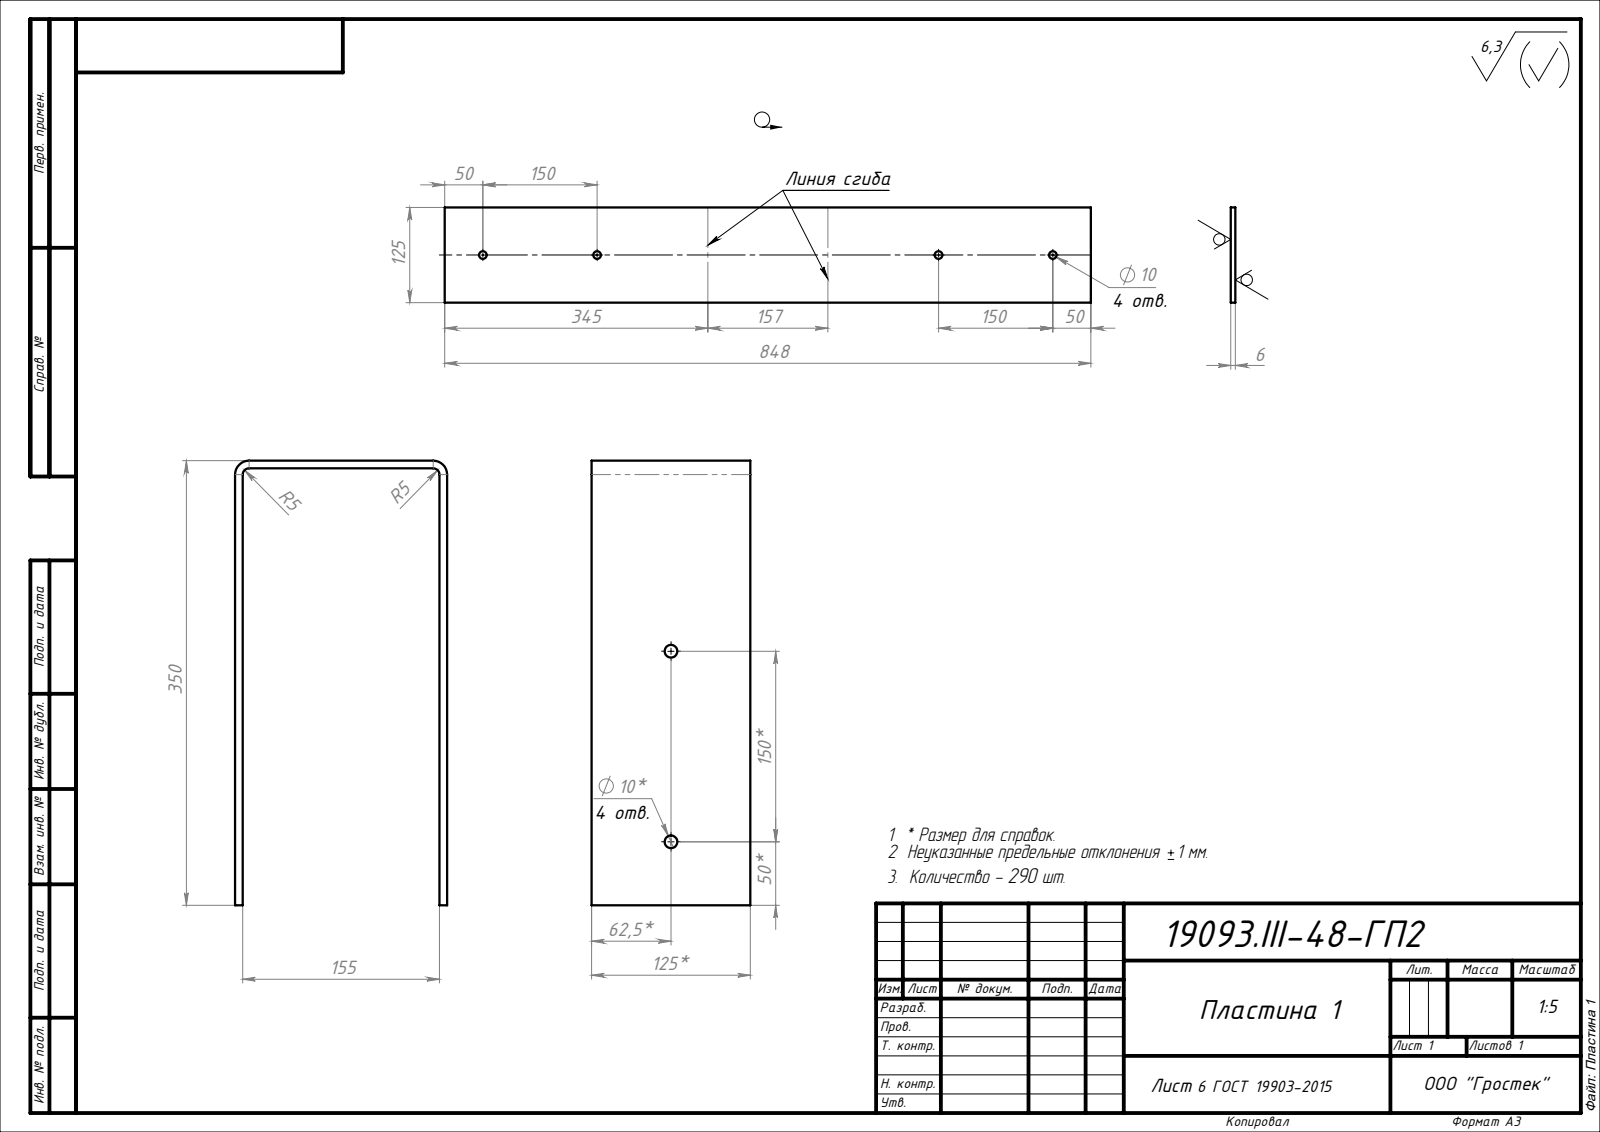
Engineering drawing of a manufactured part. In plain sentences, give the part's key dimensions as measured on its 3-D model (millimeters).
The part is named "Пластина". Its 3-D file was written by "SolidWorks 2014 (CONFIG_CONTROL_DESIGN)". It is 1 solid with 177 faces: 38 planar, 67 cylindrical and 72 other. Overall it measures 188 by 74 by 6 millimeters. Its volume is 29 791 cubic millimeters and its surface area 17 868 square millimeters. Round holes: 15 of diameter 2.5, 3 of diameter 3.5, 2 of diameter 6, 1 of diameter 2.05, 1 of diameter 60, 1 of diameter 60.05. Partial cylindrical surfaces (rounded edges, fillets, slot ends): 8 of radius 6, 4 of radius 2, 2 of radius 4. The main face-to-face distances are 6, 74, 4.5, 69.5, 177.25, 46.5, 130.75, 10.75, 57.25, 188. The hole center spacings are 50, 9.01, 35.36, 57.72, 65, 38.16, 44.23, 45.62.
